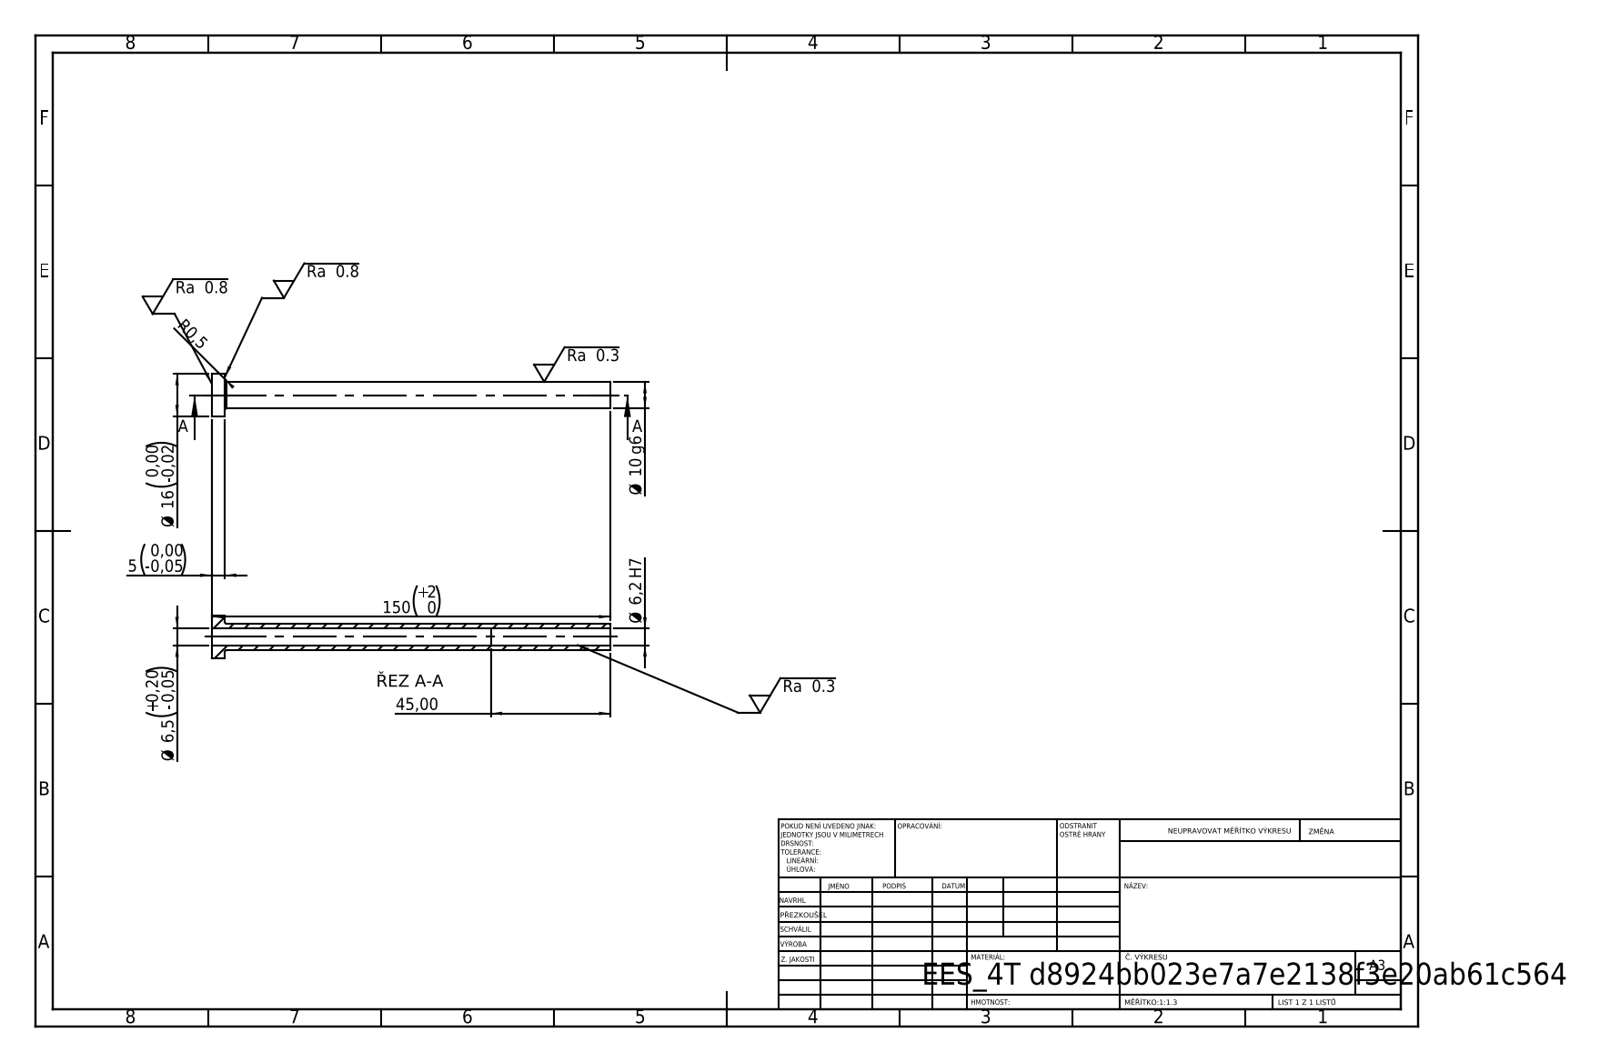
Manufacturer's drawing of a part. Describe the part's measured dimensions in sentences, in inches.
Its 3-D file was written by "SolidWorks 2019 (CONFIG_CONTROL_DESIGN)". It is 1 solid with 14 faces: 4 planar, 8 cylindrical and 2 other. Overall it measures 5.906 by 0.63 by 0.63 inches. Its volume is 0.461 cubic inches and its surface area 12.65 square inches. Round holes: 1 of diameter 0.244, 1 of diameter 0.256. Round bosses or shafts: 1 of diameter 0.63, 1 of diameter 0.394. The main face-to-face distances are 0.197, 5.906, 5.709, 4.134, 3.937, 1.772.
